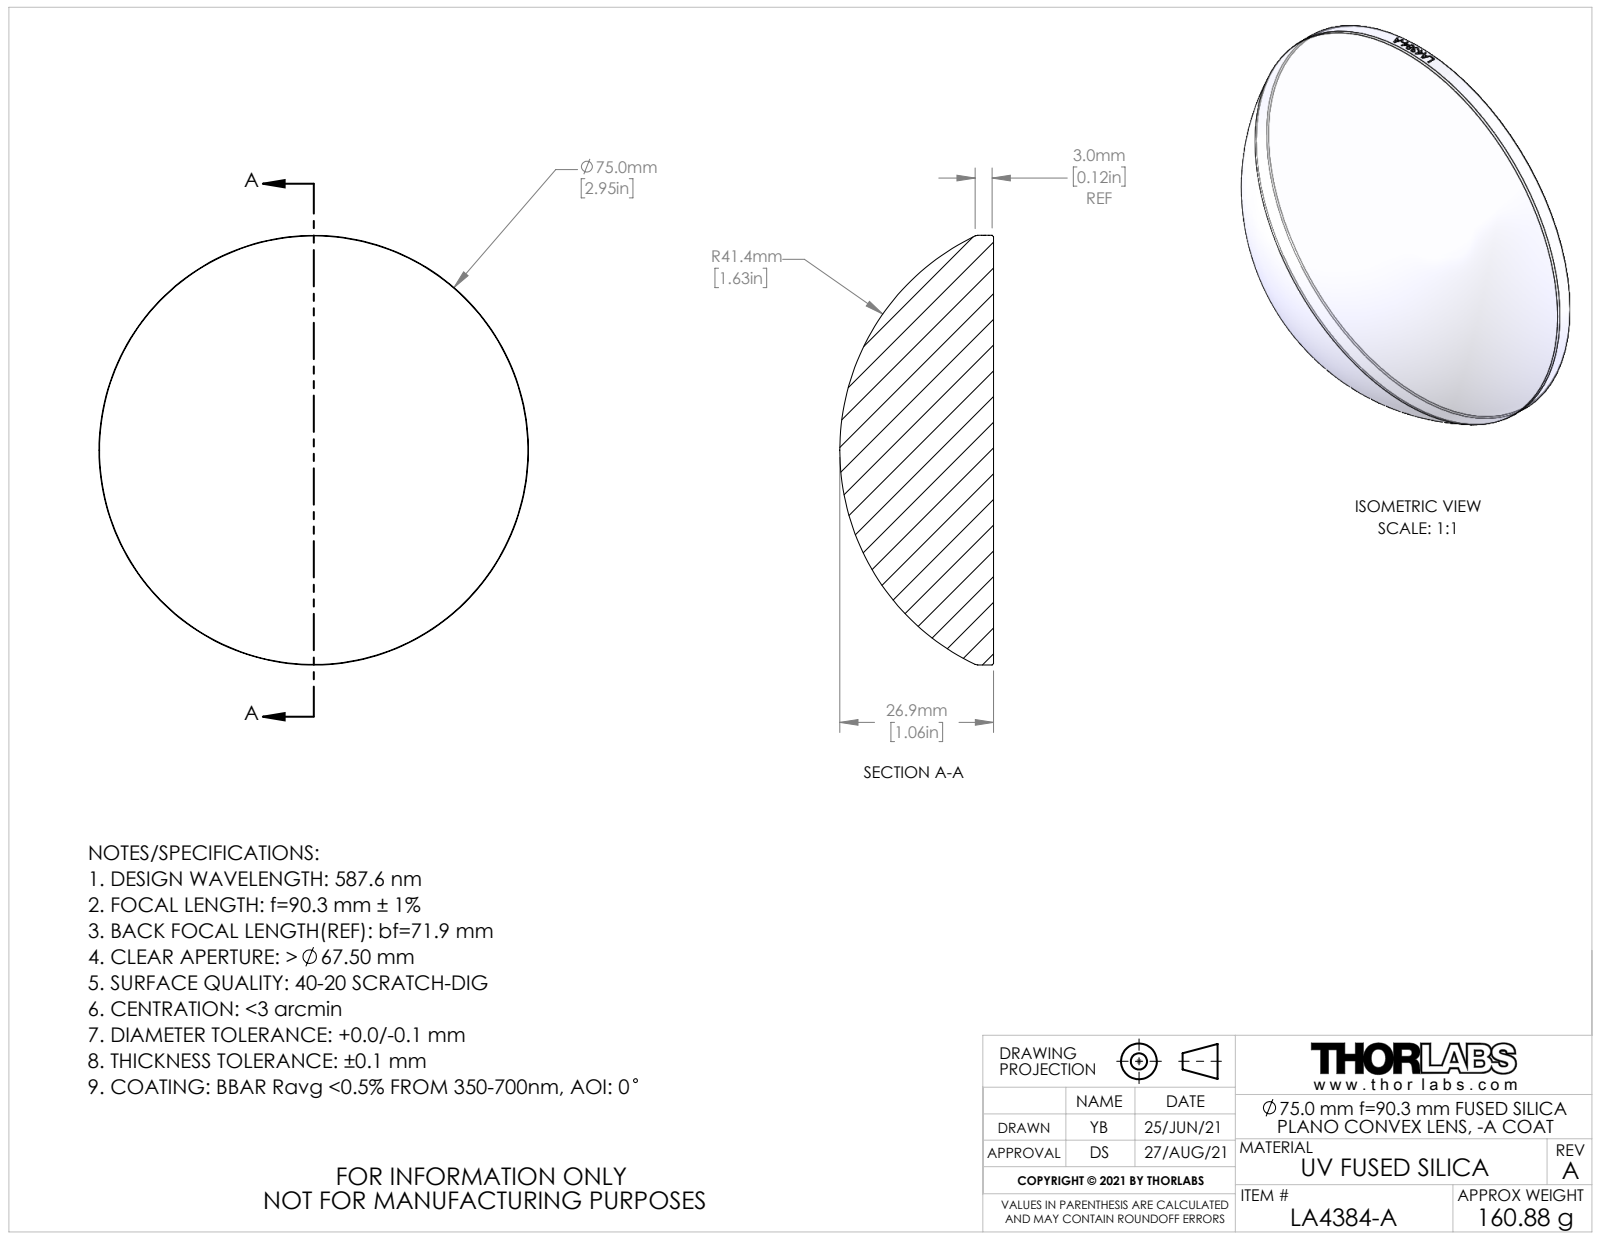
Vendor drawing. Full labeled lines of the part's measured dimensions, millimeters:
Part name (STEP PRODUCT): CTN017573; CTN017545-E0W
STEP written by: SolidWorks 2018 (AUTOMOTIVE_DESIGN)
Units: millimetres
Bodies: 1 solid, 23 faces (1 planar, 16 cylindrical, 6 other)
Overall size (bounding box): 75 × 75 × 26.85
Volume: 73 026 mm³ · Surface area: 11 292 mm²
Round bosses / shafts (diameter × count): ⌀75 ×1
